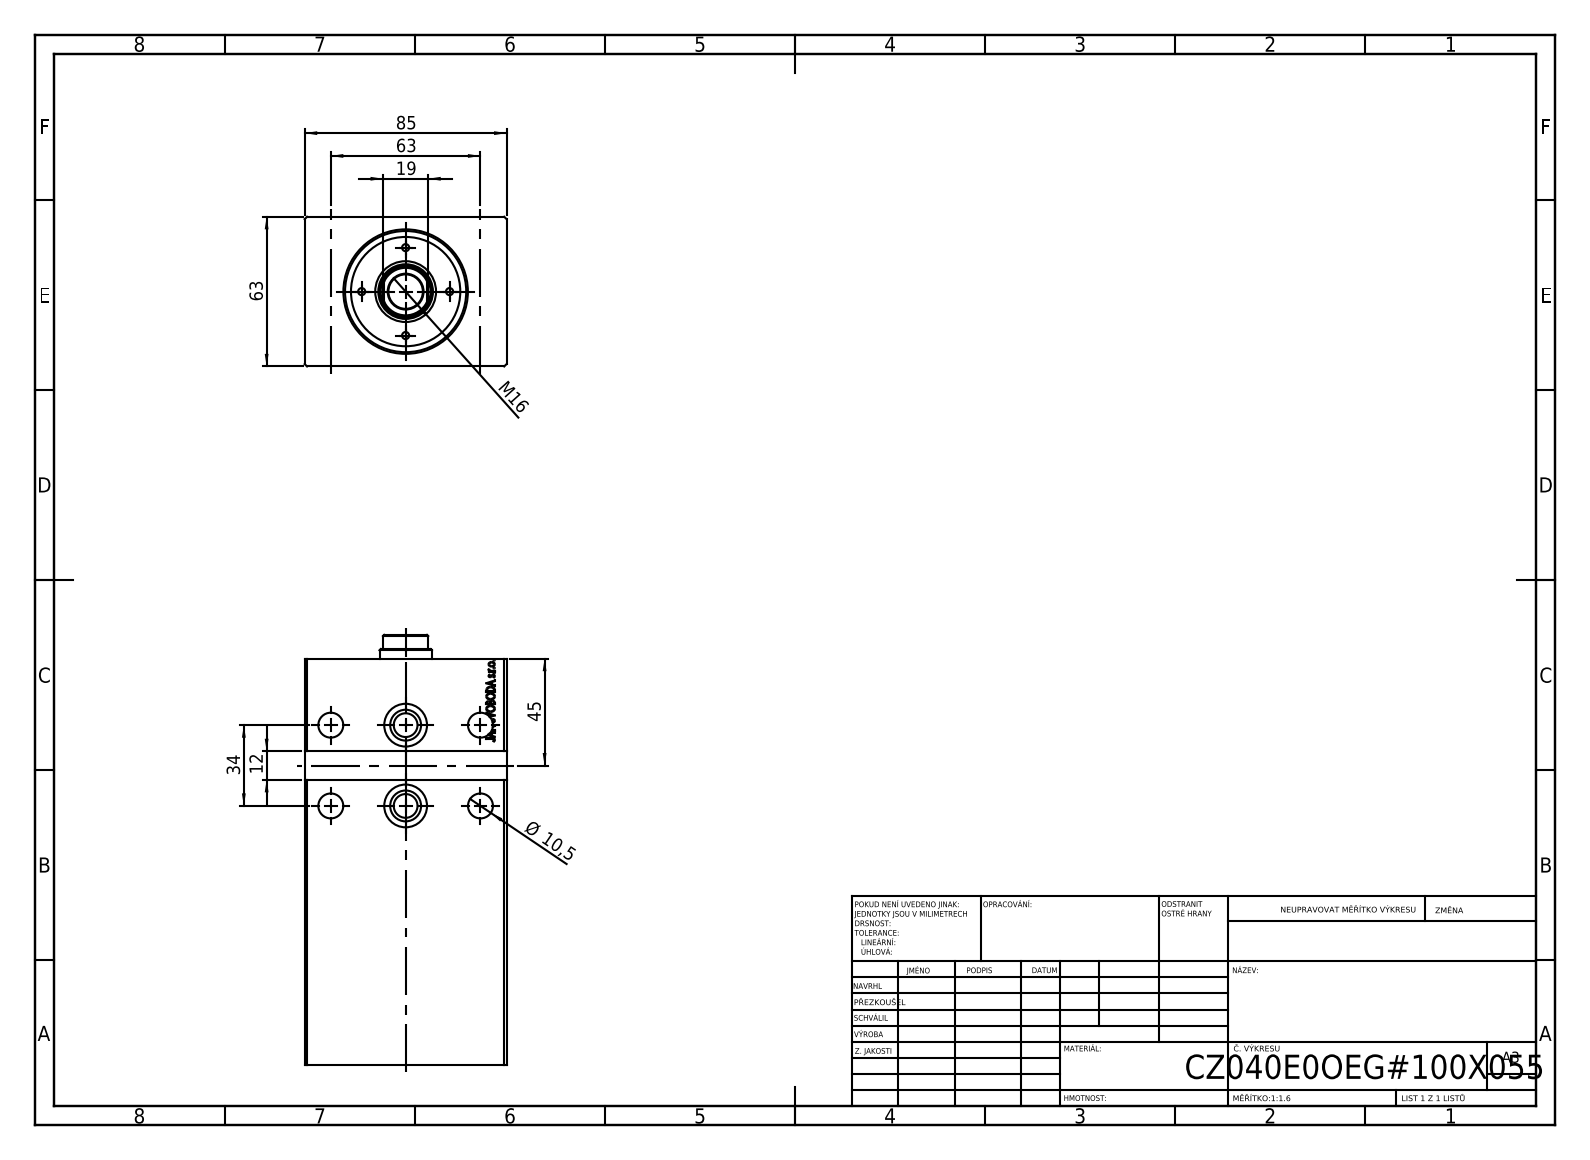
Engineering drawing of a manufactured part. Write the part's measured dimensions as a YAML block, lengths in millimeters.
step_written_by: "SolidWorks 2019 (CONFIG_CONTROL_DESIGN)"
units: millimeters
bodies: {solids: 1, faces: 779, planar: 383, cylindrical: 30, other: 366}
overall_size: [171, 85, 63]
volume: 686584
surface_area: 89450
round_holes:
  - {diameter: 10.5, count: 4}
  - {diameter: 8, count: 2}
  - {diameter: 10, count: 2}
  - {diameter: 18, count: 2}
  - {diameter: 36, count: 1}
  - {diameter: 40, count: 1}
  - {diameter: 51, count: 1}
round_bosses_or_shafts:
  - {diameter: 13, count: 2}
face_to_face_distances: [63, 85, 171, 155.7, 15.3, 2, 61, 170.8, 15.1, 10]
hole_center_spacings: [31.5, 46.35, 34, 63, 71.59, 15.65, 18.85, 30.41]
